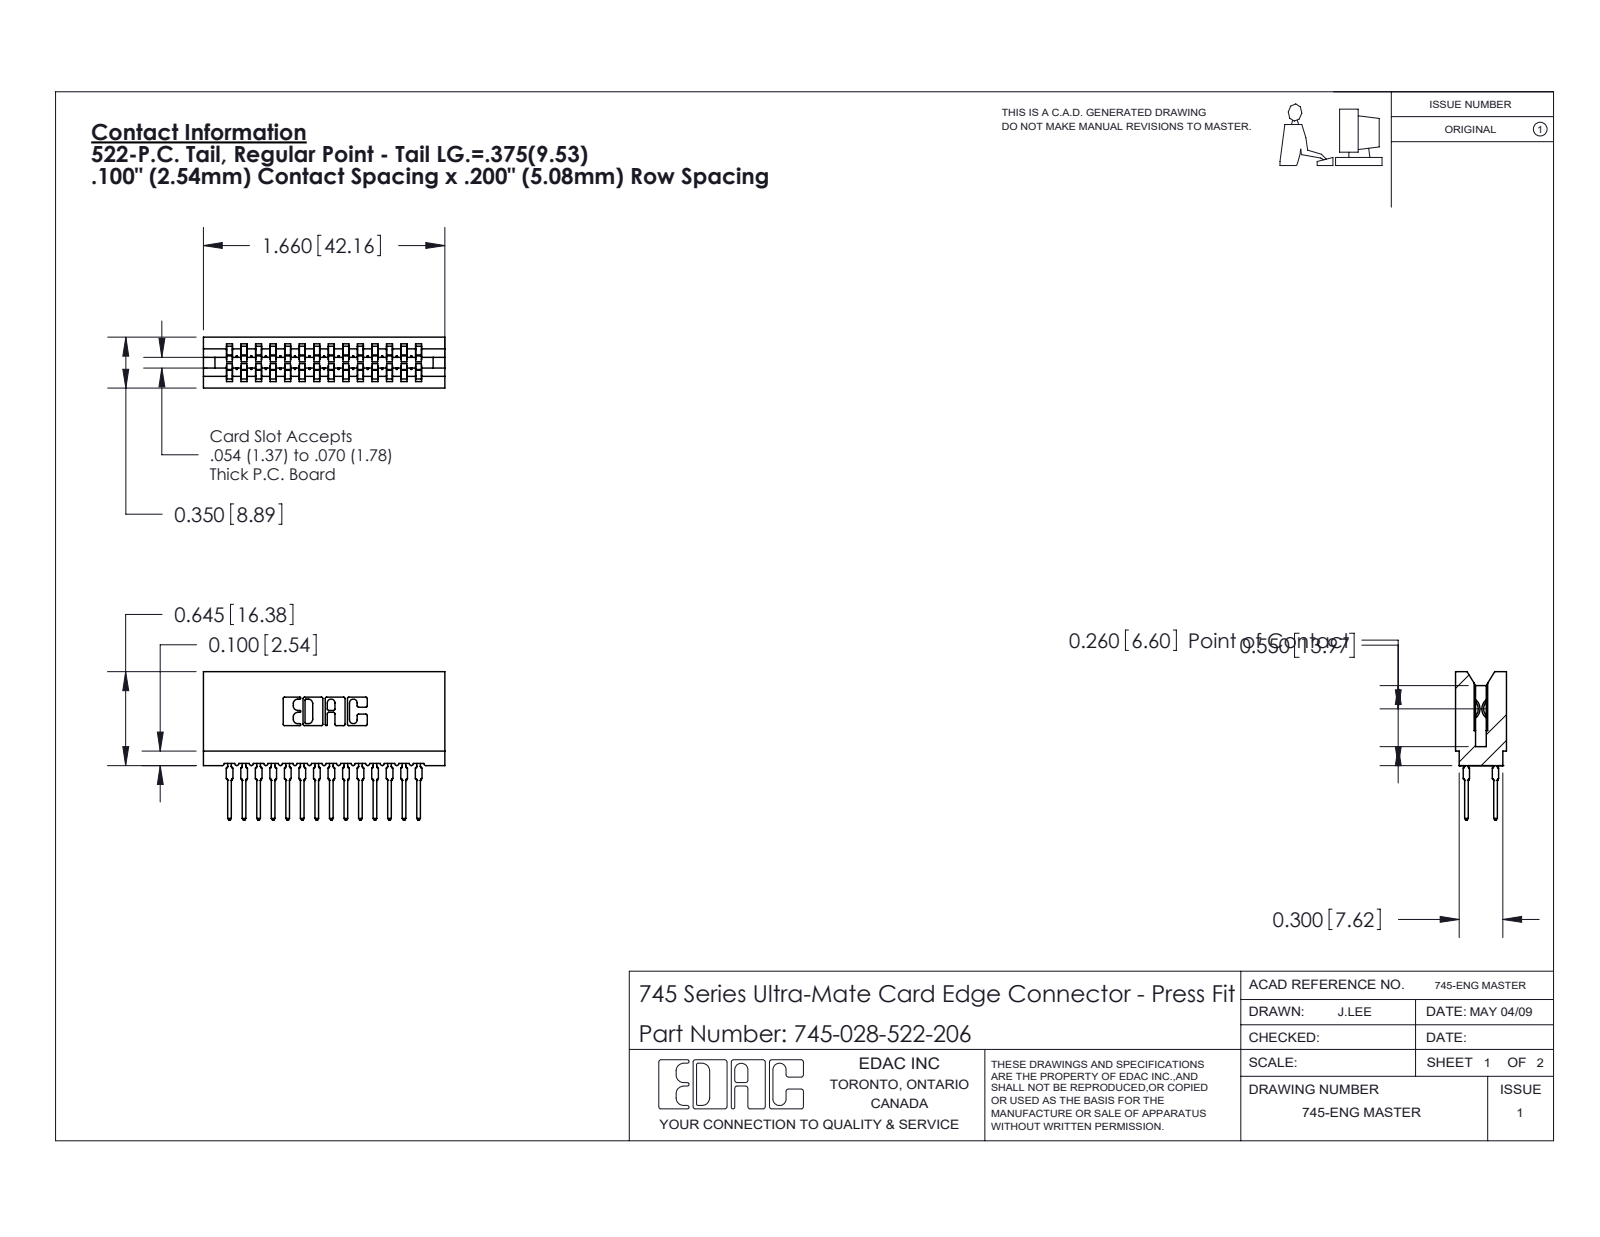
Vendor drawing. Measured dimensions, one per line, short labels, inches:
name: 745 Part_Insulator Option - 06; 745-292-001_522; 745-028-522-206
written by: SolidWorks 2020 (CONFIG_CONTROL_DESIGN)
unit: in
bodies: 29 solids, 2602 faces (1344 planar, 530 cylindrical, 728 other)
size: 1.66 × 1.021 × 0.35
volume: 0.242 in³; area: 11.71 in²
rounds: 56× R0.021, 28× R0.015, 22× R0.01, 8× R0.005, 8× R0.011, 6× R0.007, 6× R0.031, 3× R0.026
face distances: 0.2, 0.1, 0.3, 0.4, 0.5, 0.35, 0.6, 0.063, 0.287, 0.138
